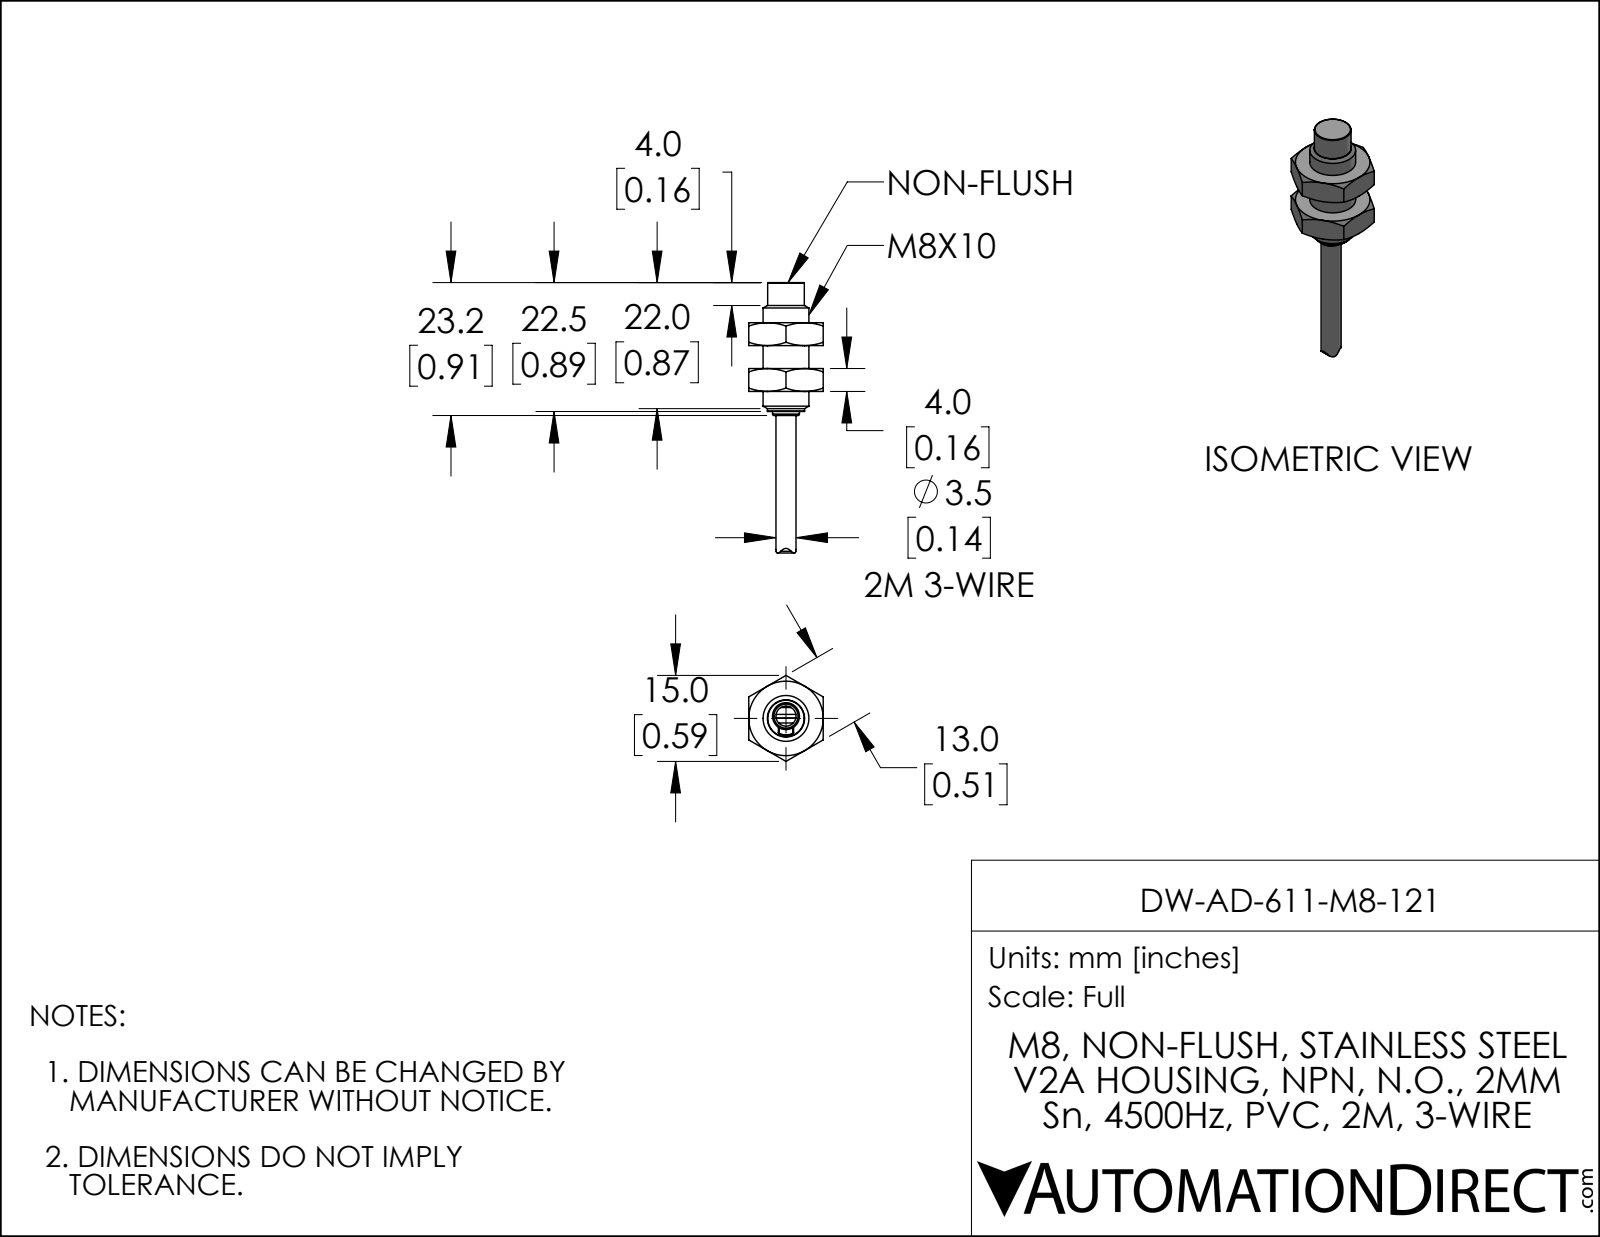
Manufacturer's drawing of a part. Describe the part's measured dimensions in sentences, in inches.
The part is named "DW-AD-611-M8-121". Its 3-D file was written by "SolidWorks 2019 (AUTOMOTIVE_DESIGN)". It is 1 solid with 78 faces: 23 planar, 19 cylindrical and 36 other. Overall it measures 1.858 by 0.591 by 0.512 inches. Its volume is 0.125 cubic inches and its surface area 2.19 square inches. Round bosses or shafts: 1 of diameter 0.315, 1 of diameter 0.256, 1 of diameter 0.252, 1 of diameter 0.185, 1 of diameter 0.138. Partial cylindrical surfaces (rounded edges, fillets, slot ends): 2 of radius 0.012, 1 of radius 0.022, 1 of radius 0.03, 1 of radius 0.116, 1 of radius 0.118, 1 of radius 0.177, 1 of radius 0.236. The main face-to-face distances are 0.157, 0.315, 0.512, 0.472, 0.276, 0.433, 0.591, 0.748, 0.886, 0.61.
